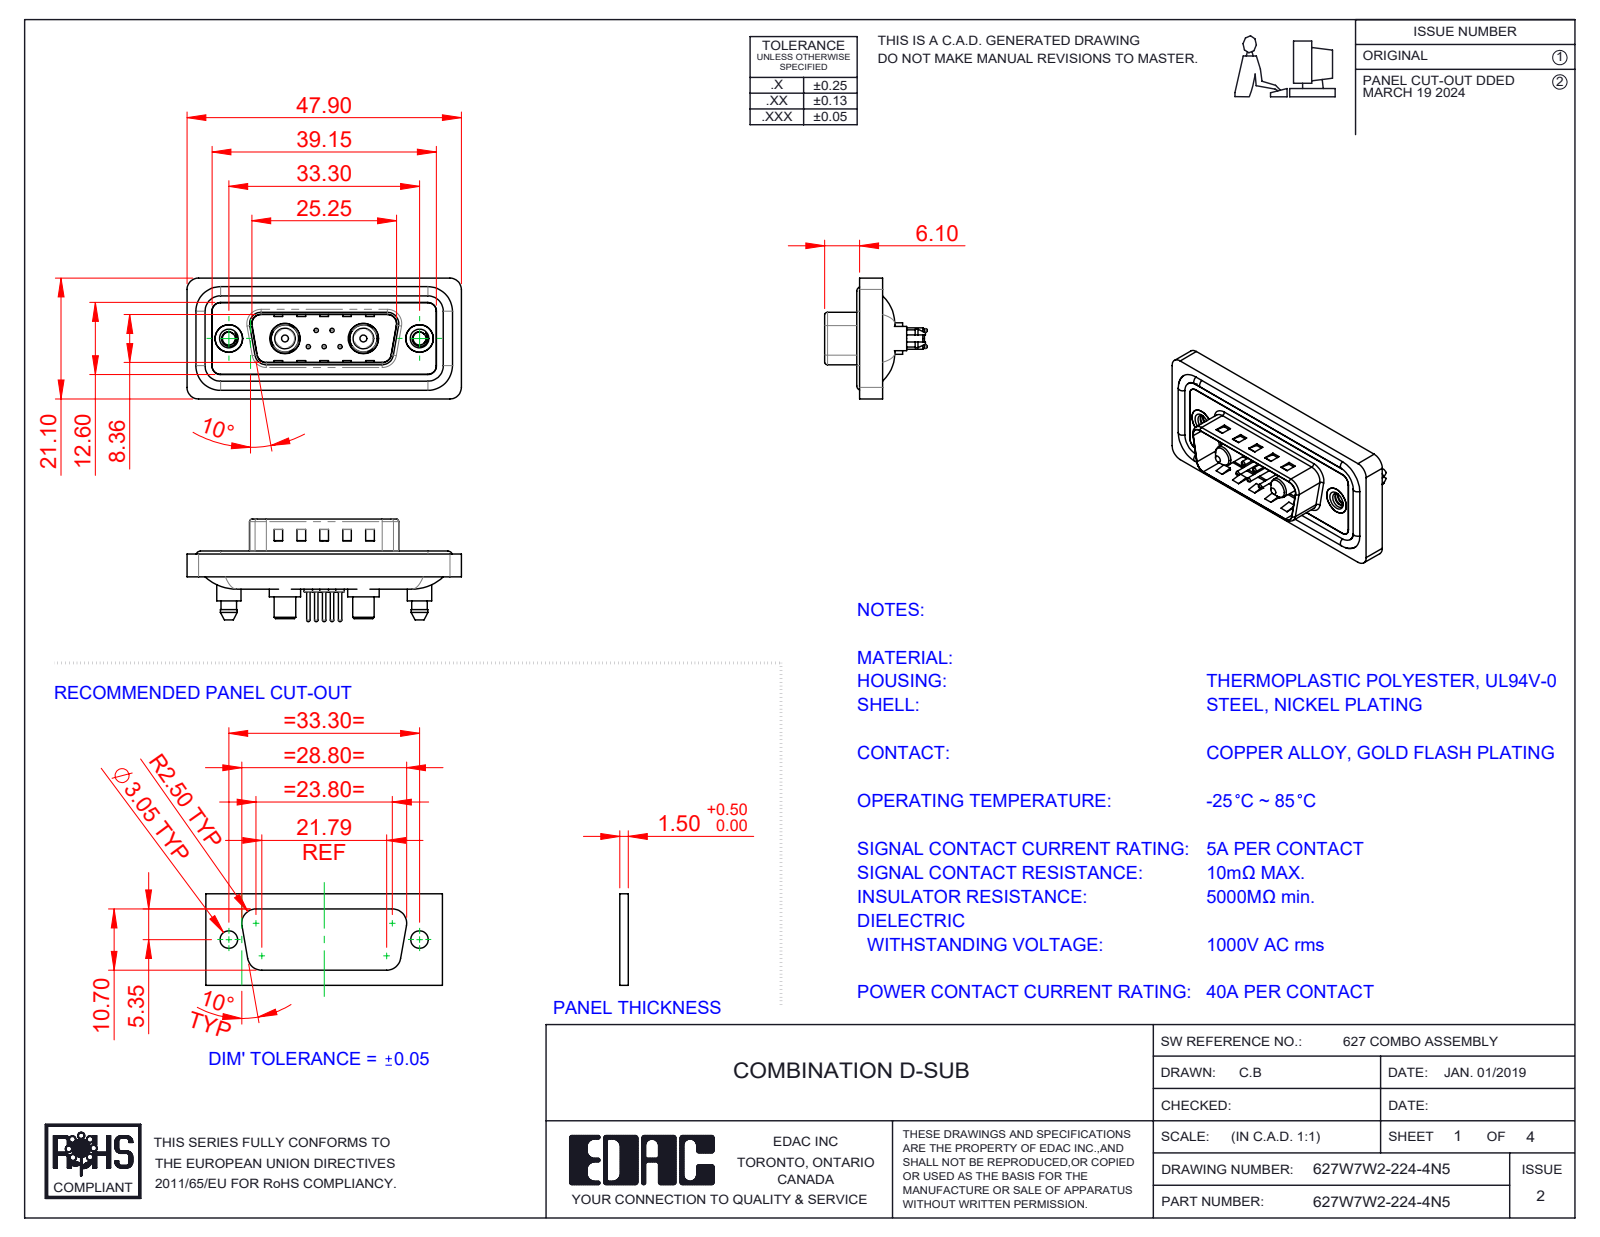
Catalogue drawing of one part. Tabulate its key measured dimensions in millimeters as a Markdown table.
| quantity | value |
| --- | --- |
| part name | 627Combo Shell Front_15 Contacts; 627Combo Contact Row 2_24; 627Combo Housing_7W2; Power Pin_40A S (+5 more) |
| STEP written by | SolidWorks 2023 (CONFIG_CONTROL_DESIGN) |
| units | millimeters |
| bodies | 16 solids, 760 faces (248 planar, 324 cylindrical, 188 other) |
| overall size | 47.9 × 21.1 × 17.9 |
| volume | 5 687 mm³ |
| surface area | 9 148 mm² |
| round holes (diameter × count) | 0.75 × 5, 1.6 × 5, 2 × 5, 2.26 × 2, 4 × 2, 4.8 × 2, 4.85 × 2, 5 × 2, 5.3 × 2 |
| round bosses / shafts (diameter × count) | 1.5 × 5, 0.6 × 5, 1.6 × 4, 5.5 × 2, 5.4 × 2, 5.2 × 2, 4.9 × 2, 4.75 × 2 |
| partial cylindrical surfaces (radius × count) | 1.5 × 28, 2 × 20, 1.6 × 10, 0.5 × 8, 0.25 × 4, 0.6 × 4, 0.65 × 4, 0.9 × 4 |
| main face-to-face distances | 0.4, 1.1, 1.6, 1.5, 3.1, 0.5, 2.9, 0.7, 0.82, 9.58 |
| hole center spacings | 3.16, 2.77, 9.8, 23.5, 4.31, 4.33, 5.03, 5.04 |
